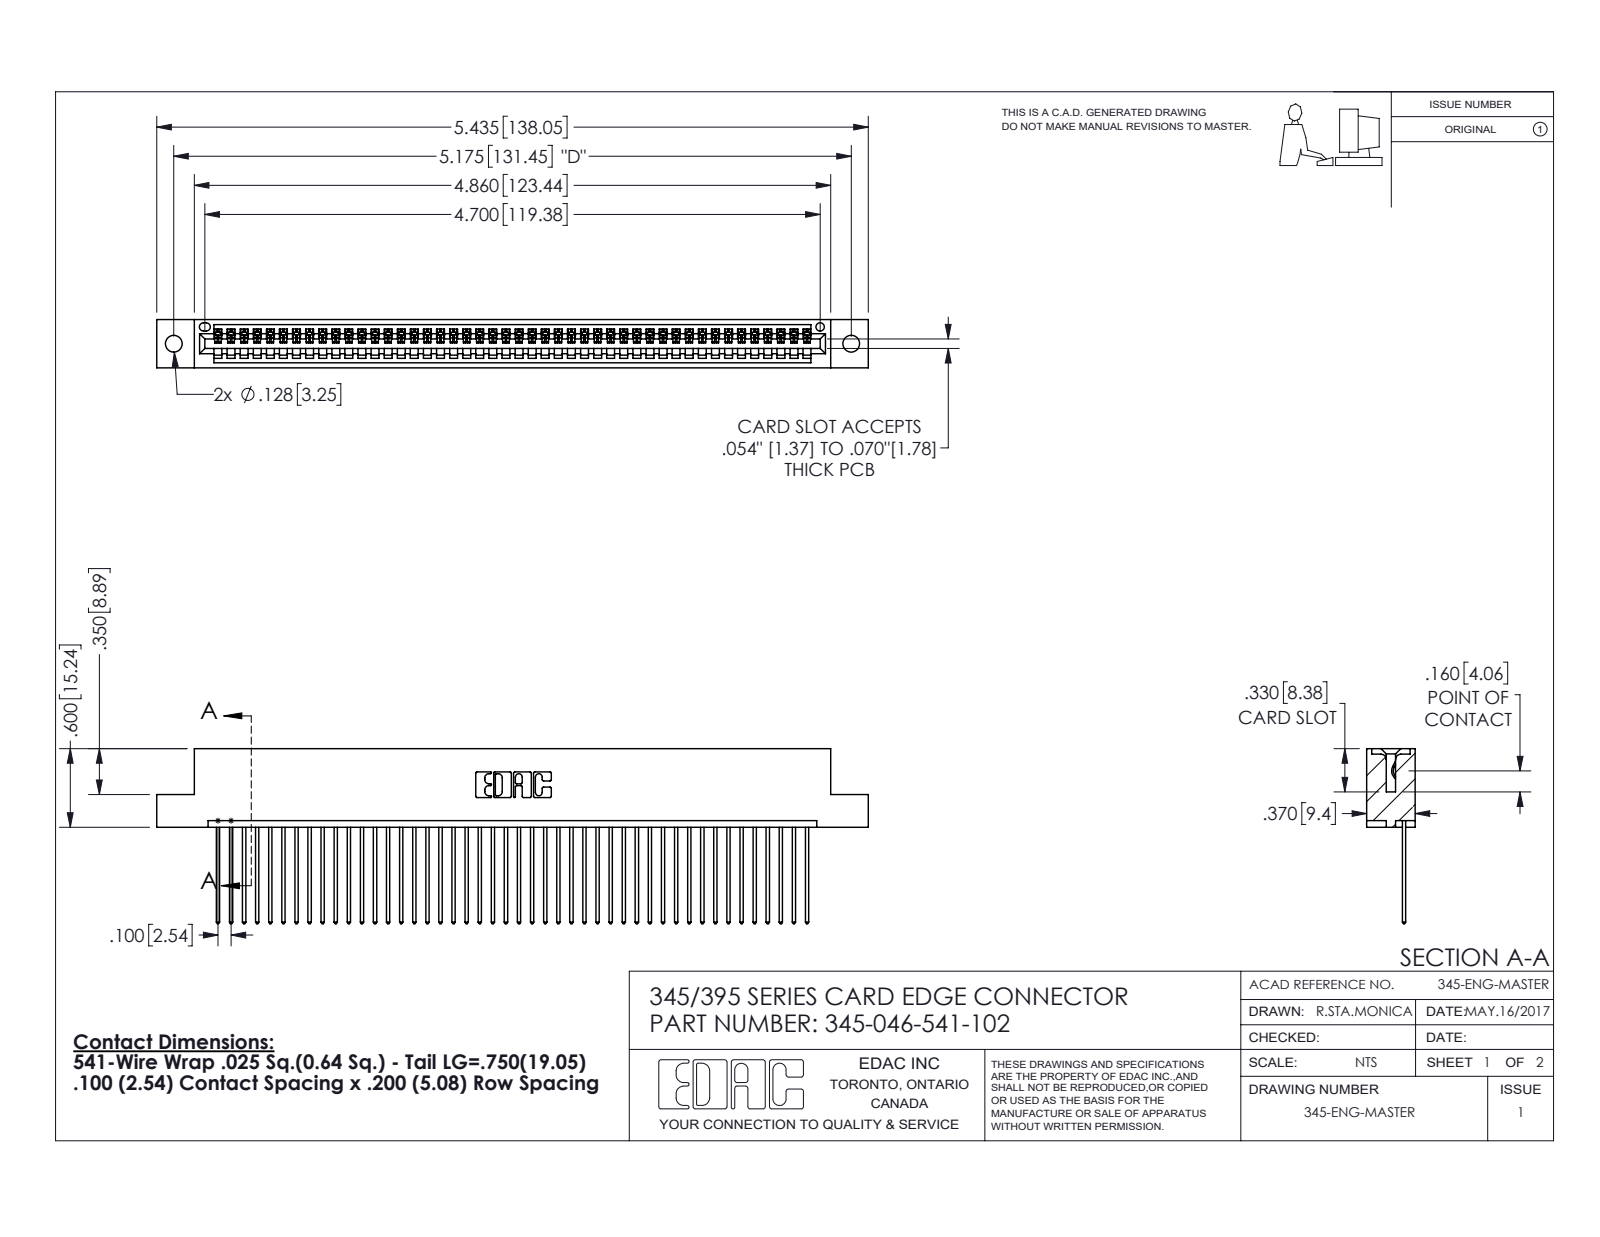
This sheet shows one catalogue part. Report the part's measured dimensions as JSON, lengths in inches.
{"part_name": "345-046-541-102; 345-292-001_345-293-141; 345 Part_Flush Mounting Lugs - 0.128 Dia", "step_written_by": "SolidWorks 2016 (CONFIG_CONTROL_DESIGN)", "units": "inches", "bodies": {"solids": 47, "faces": 2794, "planar": 1920, "cylindrical": 874, "other": 0}, "overall_size": [5.435, 1.337, 0.37], "volume_in3": 0.809, "surface_area_in2": 28.36, "round_holes": [[0.128, 2], [0.064, 1]], "partial_cylinders_radius": [[0.006, 92], [0.01, 92], [0.01, 22], [0.007, 6], [0.031, 6], [0.026, 3], [0.031, 2], [0.04, 2]], "face_to_face_distances": [0.072, 0.298, 0.098, 0.272, 0.025, 0.37, 0.2, 0.225, 0.149, 0.072], "hole_center_spacings": [0.27, 4.939, 5.175]}
